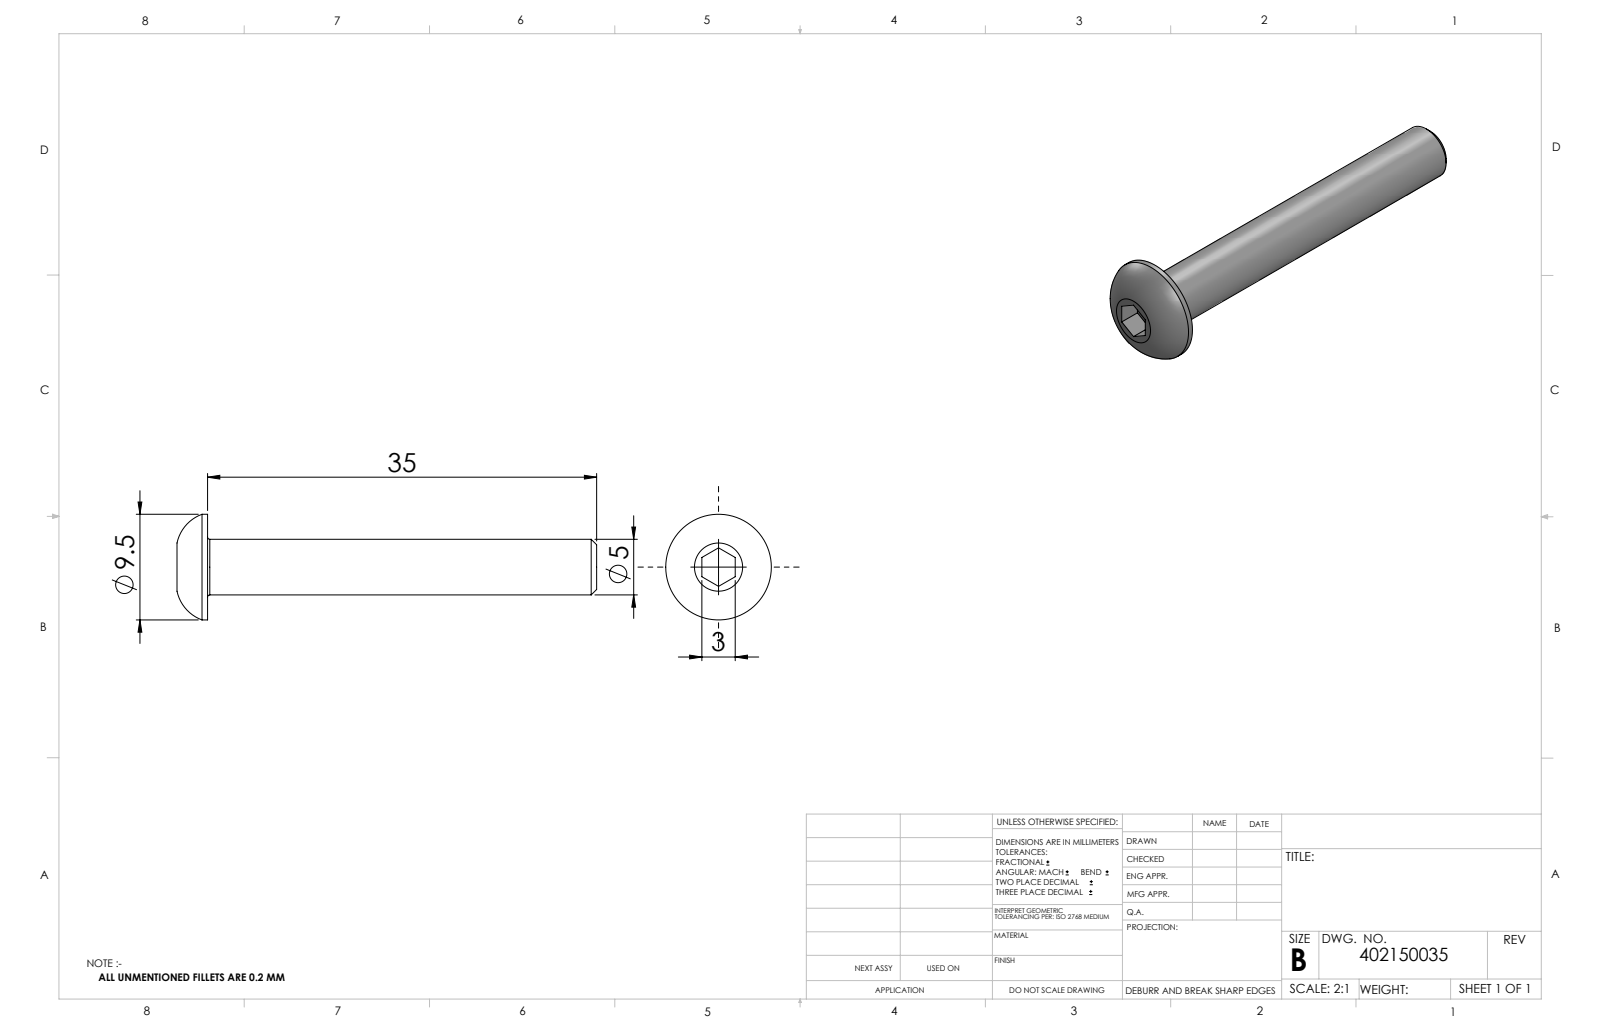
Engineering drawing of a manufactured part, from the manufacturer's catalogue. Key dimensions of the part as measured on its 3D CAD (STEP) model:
Part name (STEP PRODUCT): 402150035_c_1
STEP written by: SolidWorks 2014 (CONFIG_CONTROL_DESIGN)
Units: millimetres
Bodies: 1 solid, 20 faces (10 planar, 4 cylindrical, 6 other)
Overall size (bounding box): 37.75 × 9.5 × 9.5
Volume: 817 mm³ · Surface area: 747 mm²
Round bosses / shafts (diameter × count): ⌀9.5 ×1, ⌀5 ×1
Main face-to-face distances: 35, 3, 35.75, 0.75, 37.75, 2.75, 2
